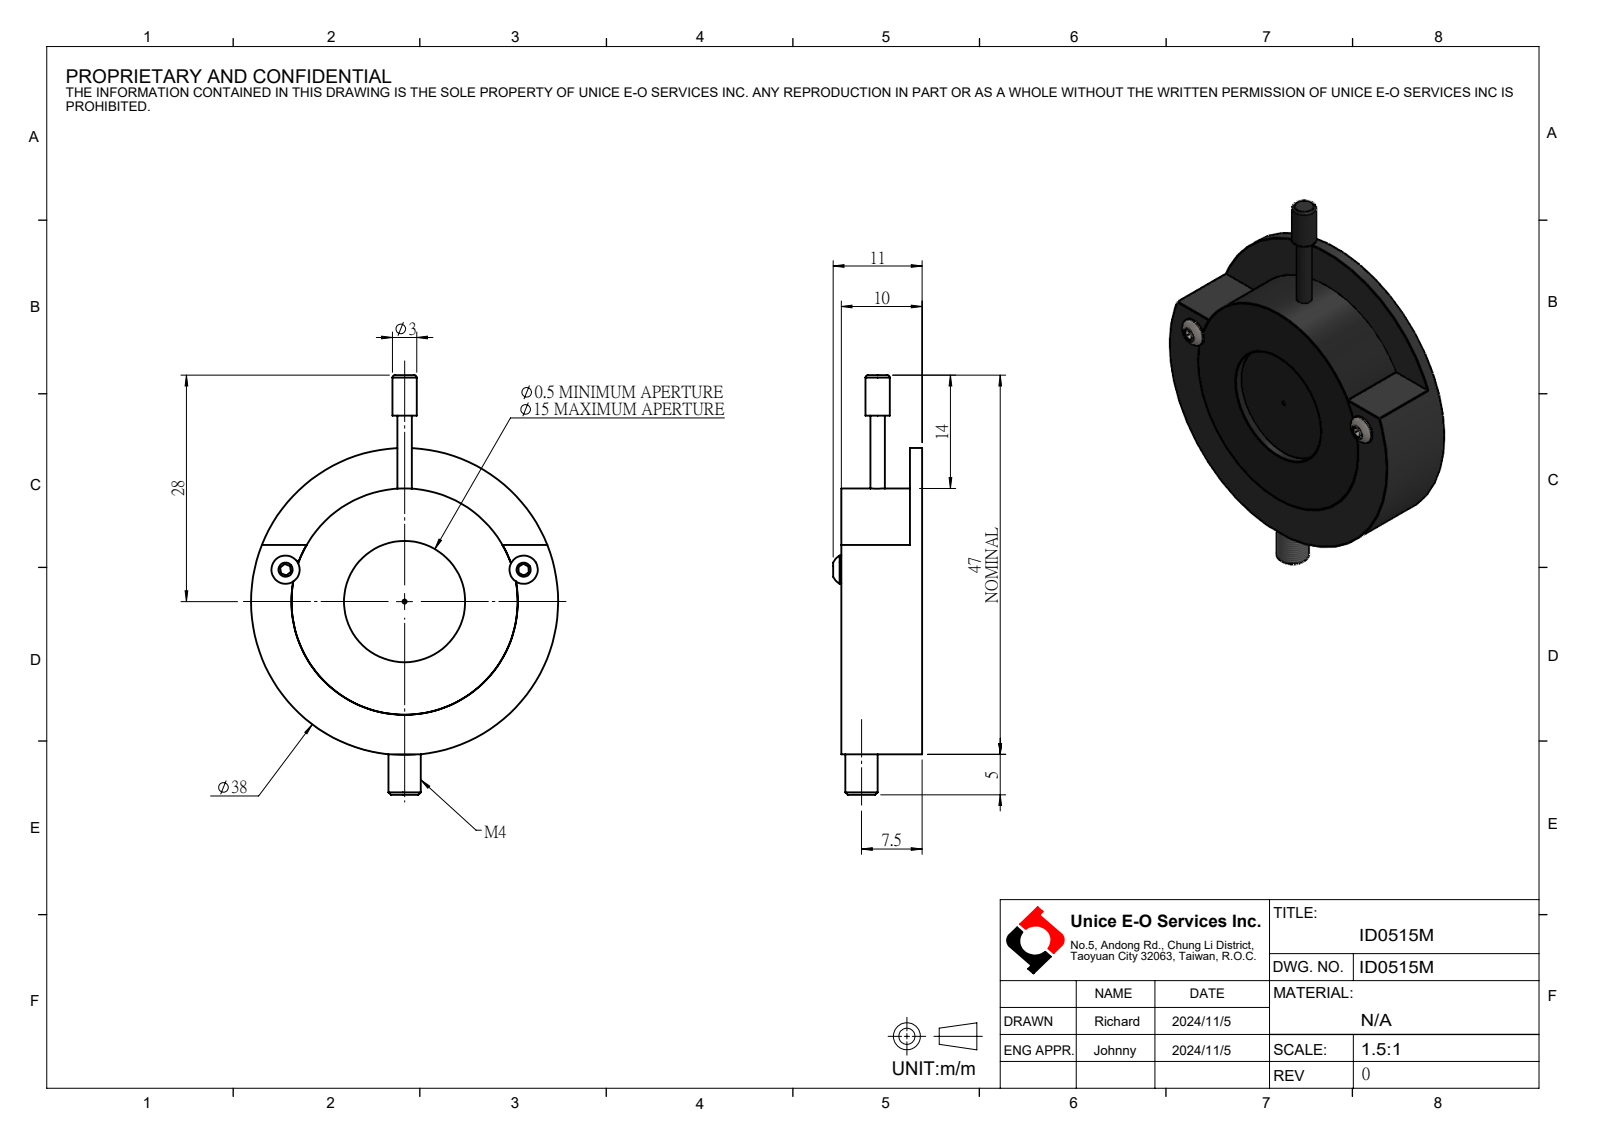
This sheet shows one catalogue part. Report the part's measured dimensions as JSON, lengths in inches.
{"part_name": "ID0515M", "step_written_by": "SolidWorks 2024 (AUTOMOTIVE_DESIGN)", "units": "inches", "bodies": {"solids": 5, "faces": 92, "planar": 43, "cylindrical": 35, "other": 14}, "overall_size": [2.043, 1.496, 0.433], "volume_in3": 0.487, "surface_area_in2": 8.745, "round_holes": [[0.063, 2], [0.02, 1], [0.13, 1], [0.591, 1], [0.984, 1], [1.102, 1]], "round_bosses_or_shafts": [[0.138, 2], [0.079, 2], [1.496, 1], [0.157, 1], [0.118, 1], [0.071, 1]], "face_to_face_distances": [0.039, 0.354, 0.394, 0.315, 0.059, 0.02, 0.335, 0.079, 0.276, 0.256], "hole_center_spacings": [0.6, 1.16]}
